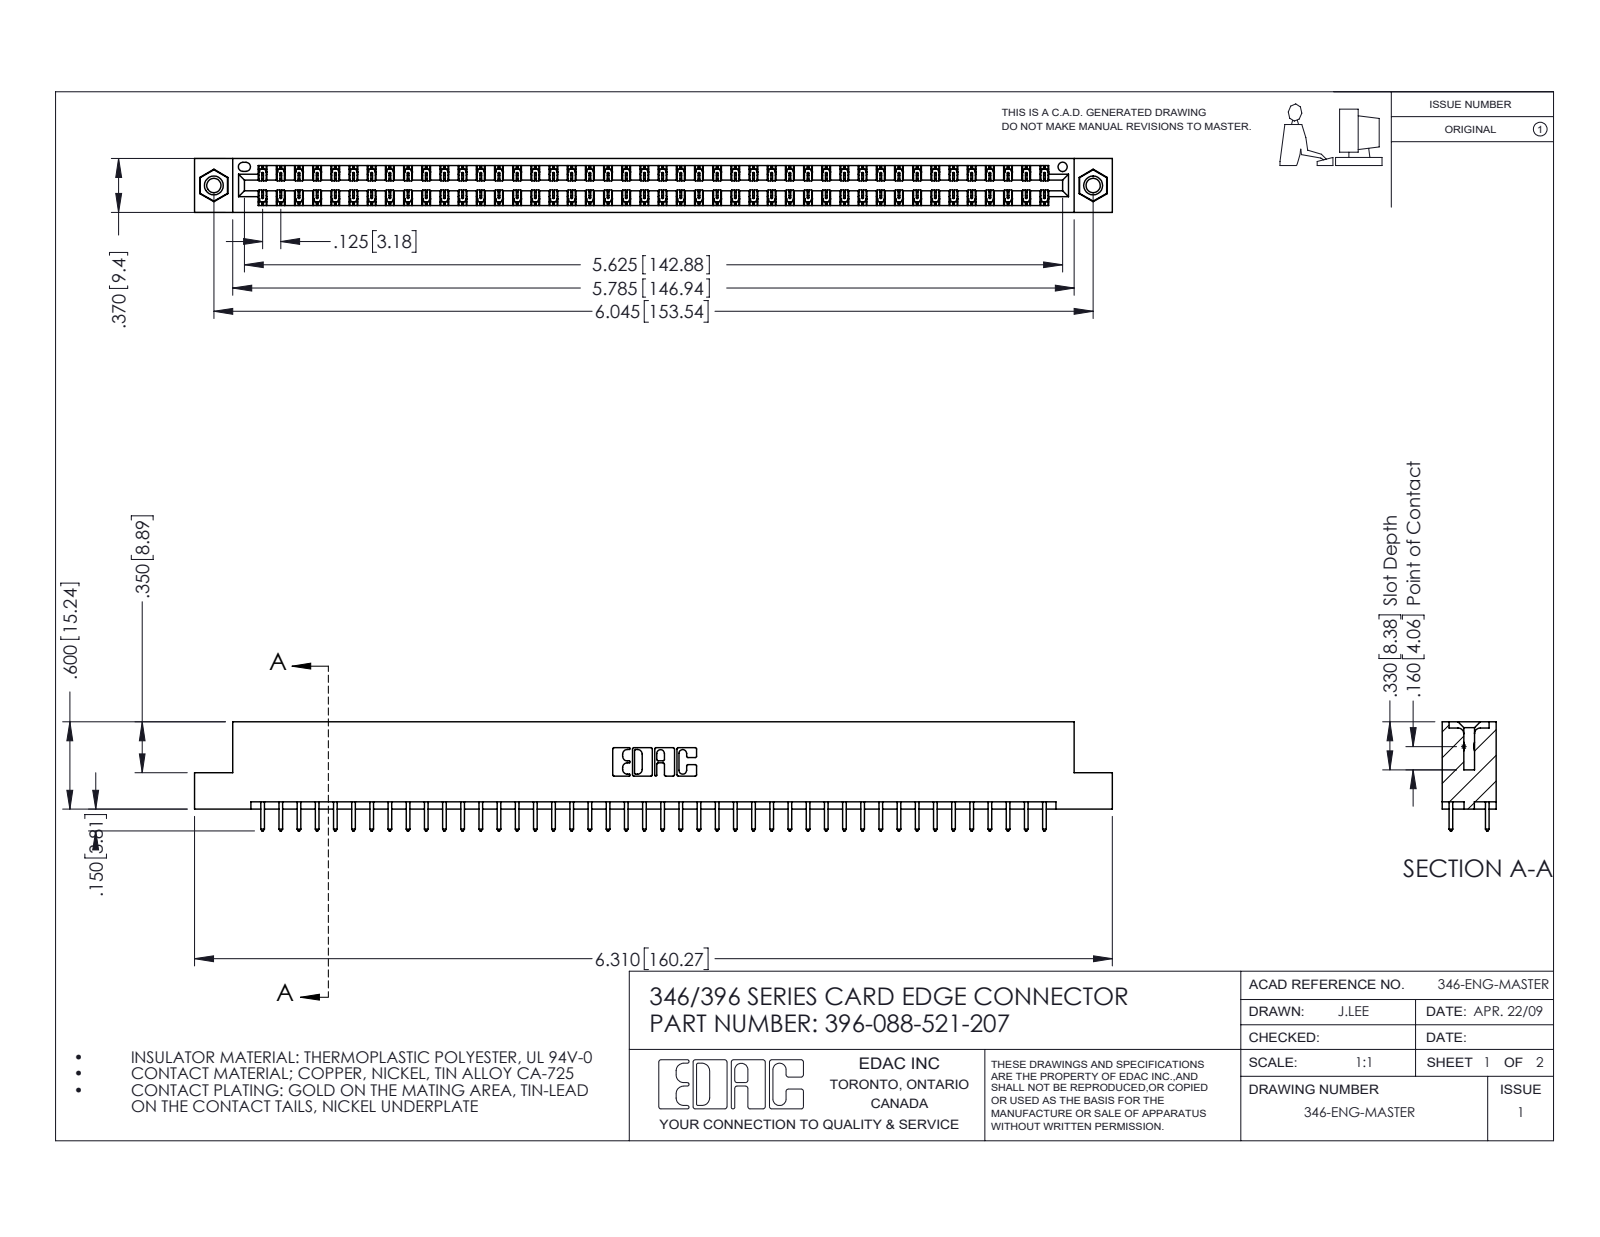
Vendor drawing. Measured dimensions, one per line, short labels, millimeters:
name: 345-292-001_345-293-121; 396-088-521-207; 346 Part_Flush Mounting Lugs - 0.156 Dia-TI; 345-250-001_345-250-005-103
written by: SolidWorks 2016 (CONFIG_CONTROL_DESIGN)
unit: mm
bodies: 91 solids, 4758 faces (3188 planar, 1554 cylindrical, 16 other)
size: 160.3 × 19.1 × 9.4
volume: 15 600 mm³; area: 21 260 mm²
holes: 2× ⌀2.5, 2× ⌀3.2, 2× ⌀4, 1× ⌀1.6
bosses: 2× ⌀3.9
rounds: 132× R0.2, 88× R0.3, 22× R0.3, 6× R0.2, 6× R0.8, 3× R0.7, 2× R0.4, 2× R0.6
face distances: 1.2, 8.2, 9.4, 6.4, 1.8, 7.6, 0.6, 7, 3.8, 5.6
hole spacings: 6.2, 148.2, 153.5
